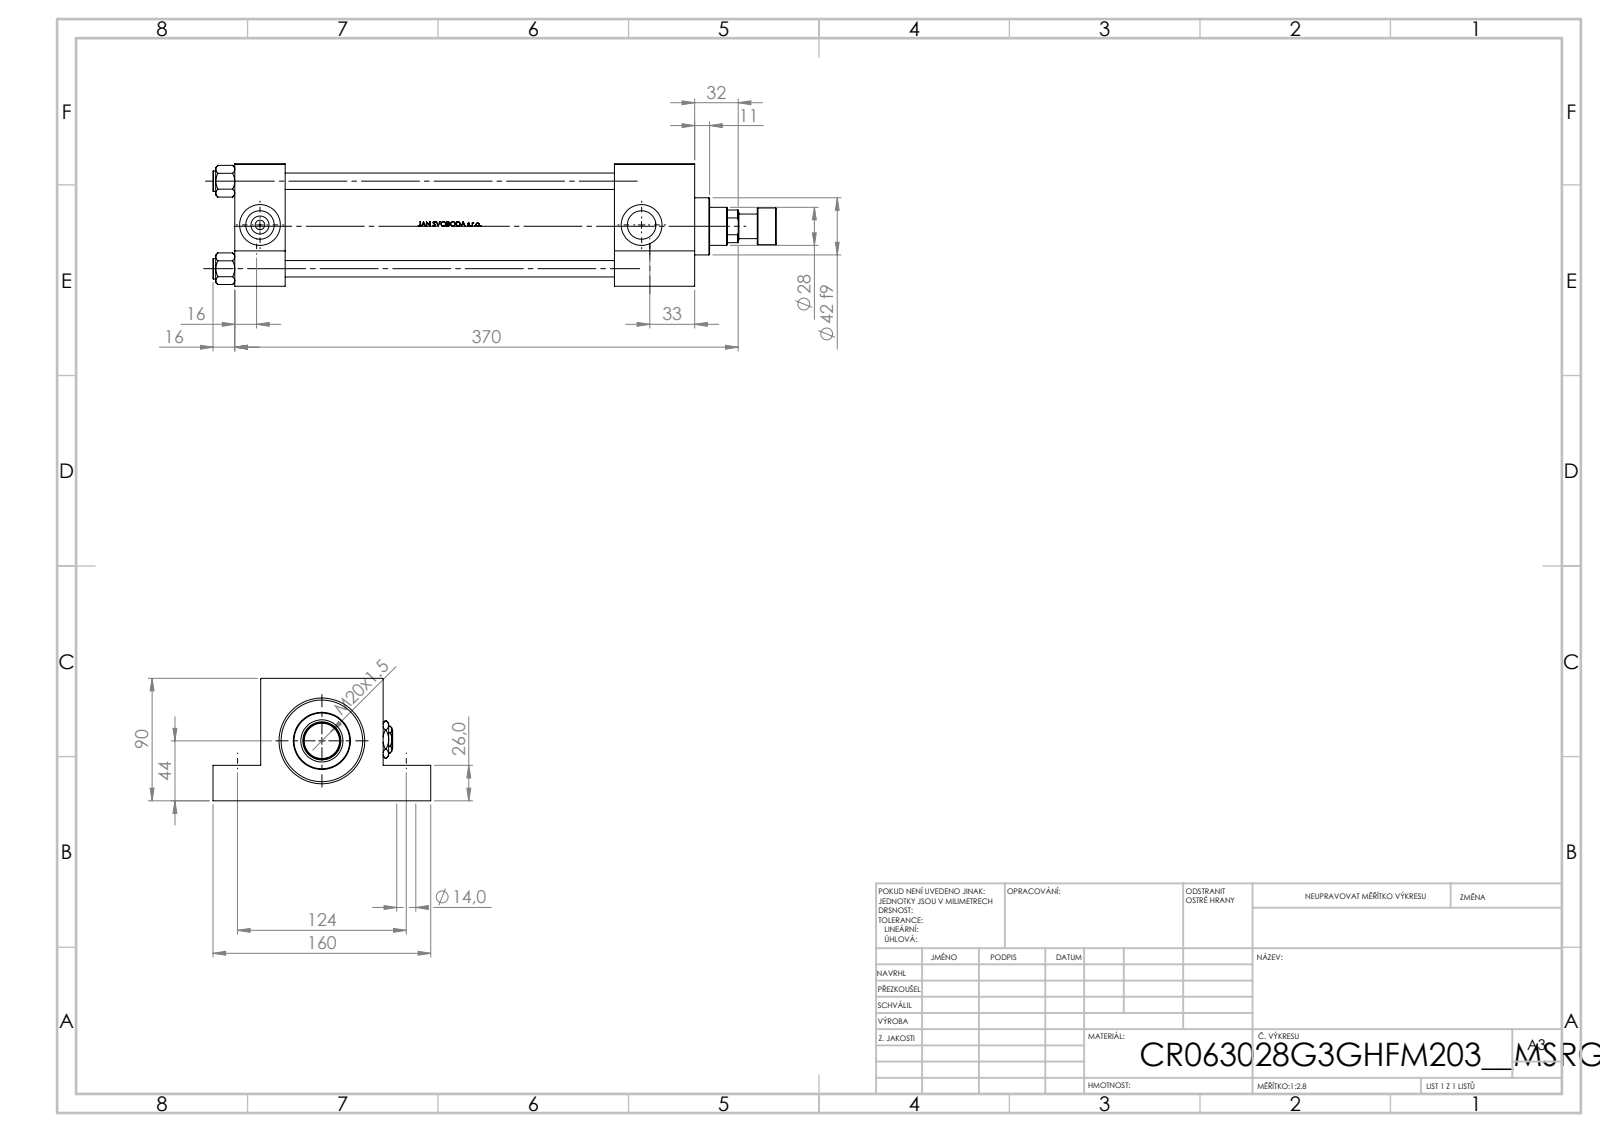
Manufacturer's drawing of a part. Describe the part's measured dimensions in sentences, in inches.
The part is named "V215CR_ROD_END_F; NUT_M5_G; V215_VC_A; V215CR_G_TYCINKA (+3 more)". Its 3-D file was written by "SolidWorks 2019 (CONFIG_CONTROL_DESIGN)". It is 14 solids with 1198 faces: 482 planar, 136 cylindrical and 580 other. Overall it measures 16.299 by 6.299 by 3.543 inches. Its volume is 87.32 cubic inches and its surface area 507.1 square inches. Round holes: 4 of diameter 0.472, 4 of diameter 0.551, 2 of diameter 0.276, 2 of diameter 0.825, 2 of diameter 1.181, 1 of diameter 0.728, 1 of diameter 1.102, 1 of diameter 1.22, 1 of diameter 1.969, 1 of diameter 2.362, 1 of diameter 2.48. Round bosses or shafts: 4 of diameter 0.591, 1 of diameter 2.717, 1 of diameter 1.654, 1 of diameter 1.063, 1 of diameter 0.709. The main face-to-face distances are 3.543, 1.457, 11.85, 13.307, 2.323, 10.984, 9.528, 2.52, 1.024, 1.378. The hole center spacings are 2.531, 1.763, 1.818, 3.58, 4.882, 11.378, 12.381, 11.043.
